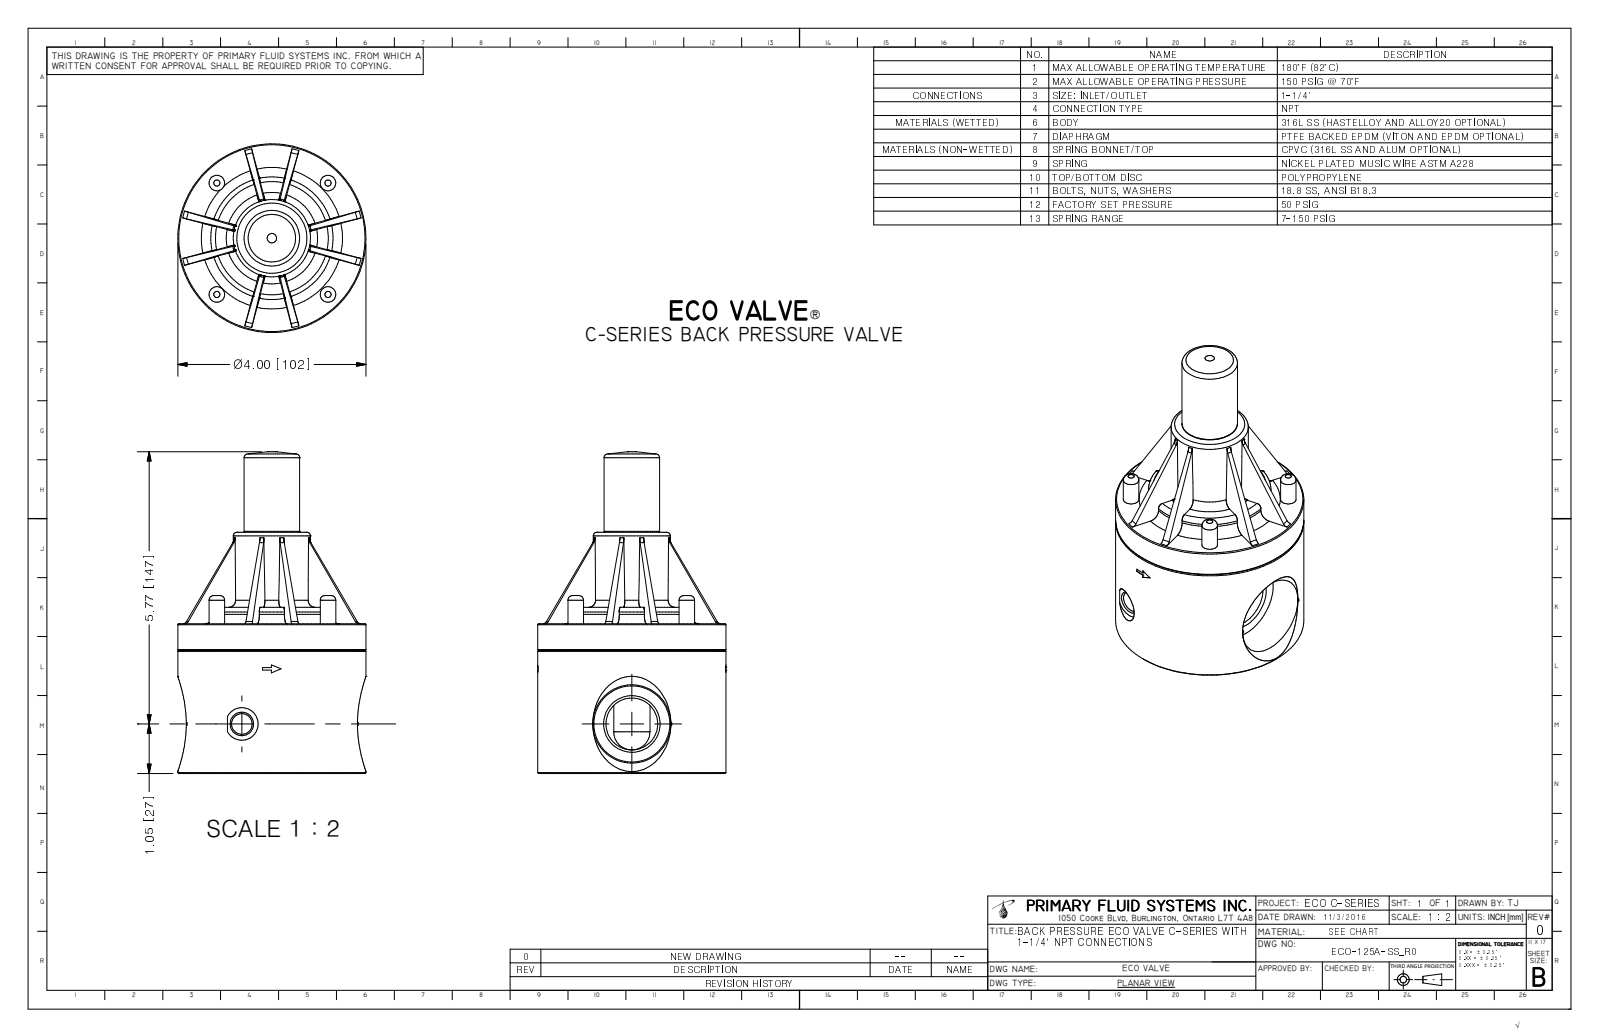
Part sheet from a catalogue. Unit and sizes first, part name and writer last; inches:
Units: inches
Overall size (bounding box): 6.824 × 4 × 4
Round holes (diameter × count): ⌀0.23 ×4, ⌀0.4 ×4, ⌀0.257 ×1, ⌀0.438 ×1, ⌀0.691 ×1
Round bosses / shafts (diameter × count): ⌀0.33 ×4, ⌀0.256 ×4, ⌀4 ×1, ⌀2.6 ×1, ⌀1.64 ×1, ⌀1.18 ×1
Partial cylindrical surfaces — rounded edges, fillets, slot ends (radius × count): R0.1 ×8, R0.128 ×4, R0.129 ×3, R0.2 ×3, R1.999 ×1
Main face-to-face distances: 3.174, 2.2, 3.524, 0.35, 5.114, 1.94, 1.59, 0.27, 0.275, 2.899
Hole centre spacings: 2.363, 2.363, 2.386, 2.386, 0.023, 3.342, 3.358, 3.374
Volume: 43.91 in³ · Surface area: 117.7 in²
Bodies: 1 solid, 221 faces (103 planar, 52 cylindrical, 66 other)
Part name (STEP PRODUCT): ECO-125A-SS_R0
STEP written by: Autodesk Inventor 2009 (AUTOMOTIVE_DESIGN)
